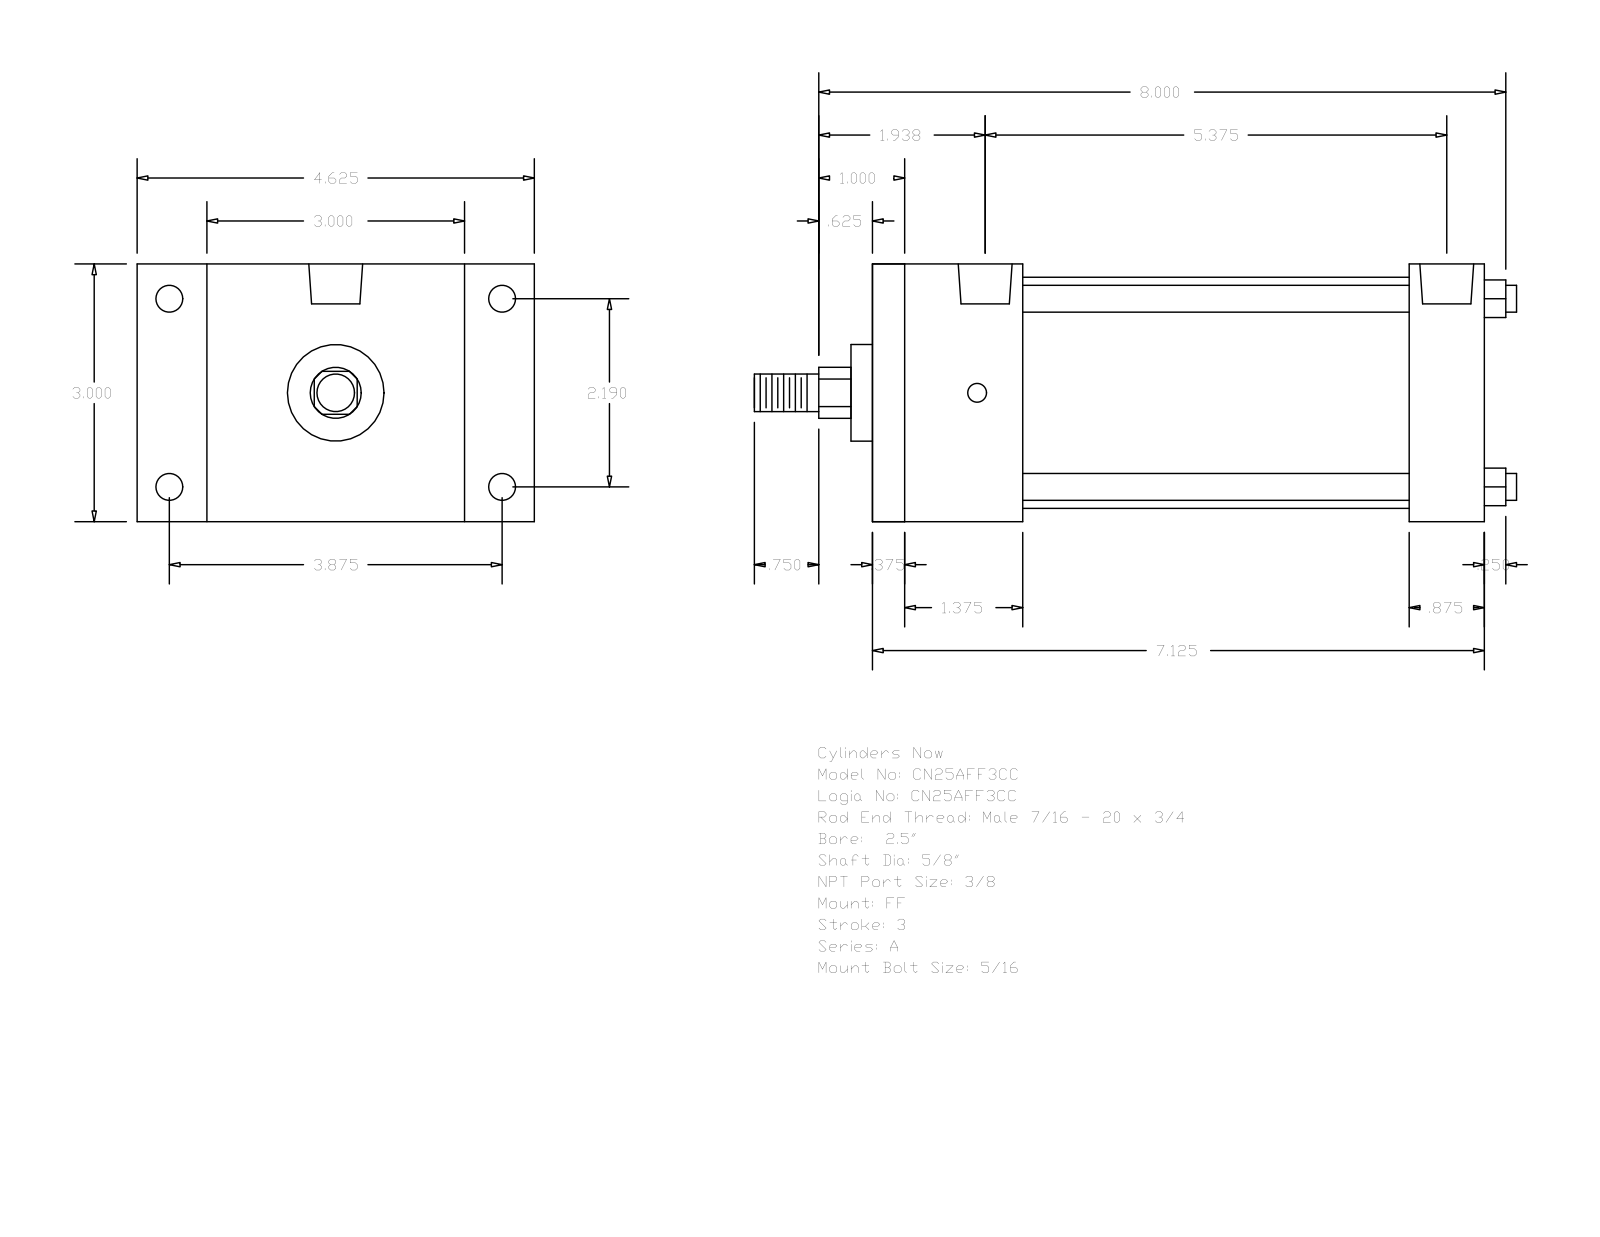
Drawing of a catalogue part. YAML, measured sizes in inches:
part_name: "A_FF__0250_0.625"
step_written_by: "GSSL Pune (CONFIG_CONTROL_DESIGN)"
units: inches
bodies: {solids: 0, faces: 92, planar: 64, cylindrical: 28, other: 0}
overall_size: [8.875, 4.625, 3]
round_holes:
  - {diameter: 0.219, count: 4}
  - {diameter: 0.313, count: 4}
  - {diameter: 0.627, count: 2}
round_bosses_or_shafts:
  - {diameter: 0.313, count: 4}
  - {diameter: 2.69, count: 1}
  - {diameter: 1.125, count: 1}
  - {diameter: 0.625, count: 1}
  - {diameter: 0.437, count: 1}
partial_cylinders:
  - {radius: 0.297, count: 1}
face_to_face_distances: [3, 7.125, 0.375, 6.75, 1.75, 1.375, 6.25, 5.875, 4.5, 5.375]
hole_center_spacings: [0.094, 2.19, 3.875, 4.451, 5.469, 5.563, 5.375]
